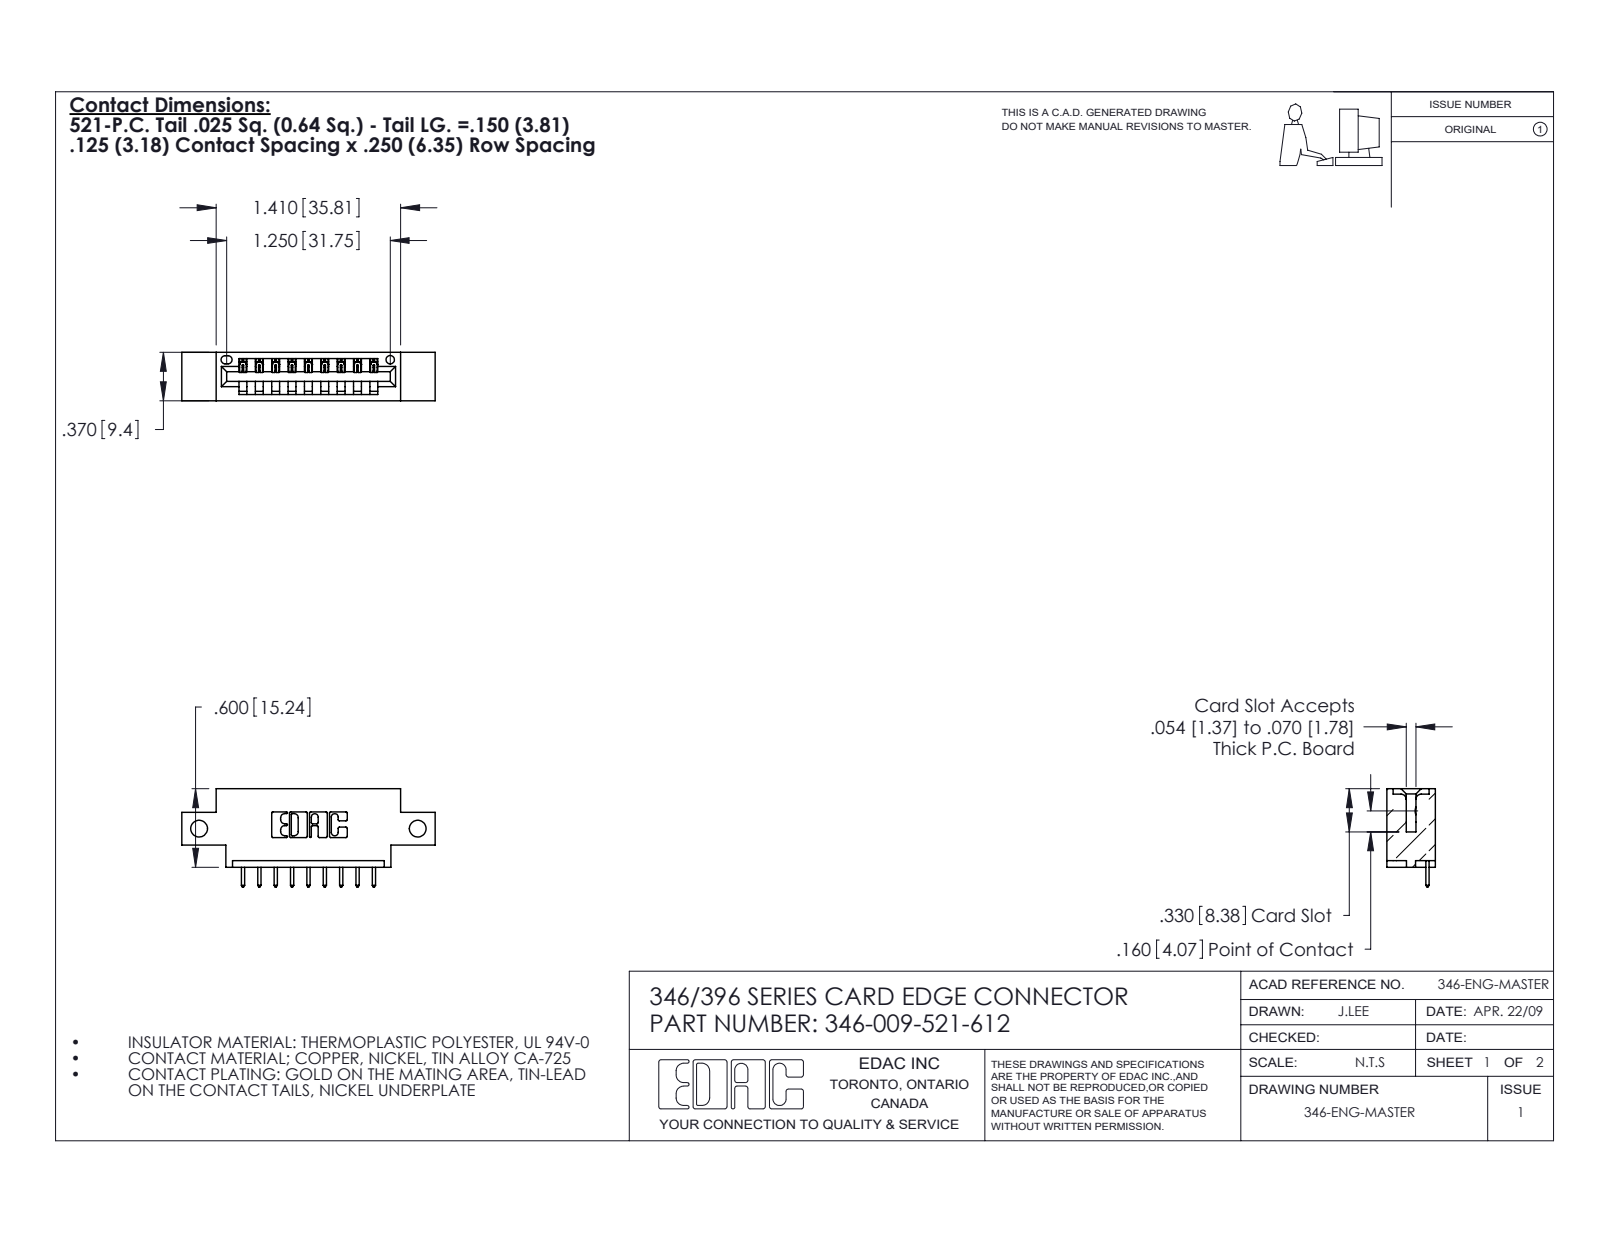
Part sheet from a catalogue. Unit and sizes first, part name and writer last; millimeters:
Units: millimetres
Overall size (bounding box): 49.1 × 19.1 × 9.4
Round holes (diameter × count): ⌀3.3 ×2, ⌀1.6 ×1
Partial cylindrical surfaces — rounded edges, fillets, slot ends (radius × count): R0.3 ×22, R0.2 ×18, R0.3 ×18, R0.2 ×6, R0.8 ×6, R0.7 ×3, R0.8 ×2, R1 ×2
Main face-to-face distances: 6.4, 9.4, 1.2, 8.2, 3.8, 5.6, 2.5, 4.4, 1.8, 7.6
Hole centre spacings: 42.4
Volume: 4 210 mm³ · Surface area: 4 818 mm²
Bodies: 10 solids, 648 faces (440 planar, 208 cylindrical, 0 other)
Part name (STEP PRODUCT): 345-292-001_345-293-121; 346 Part_0.170 Offset - Side Mount; 346-009-521-612
STEP written by: SolidWorks 2020 (CONFIG_CONTROL_DESIGN)
